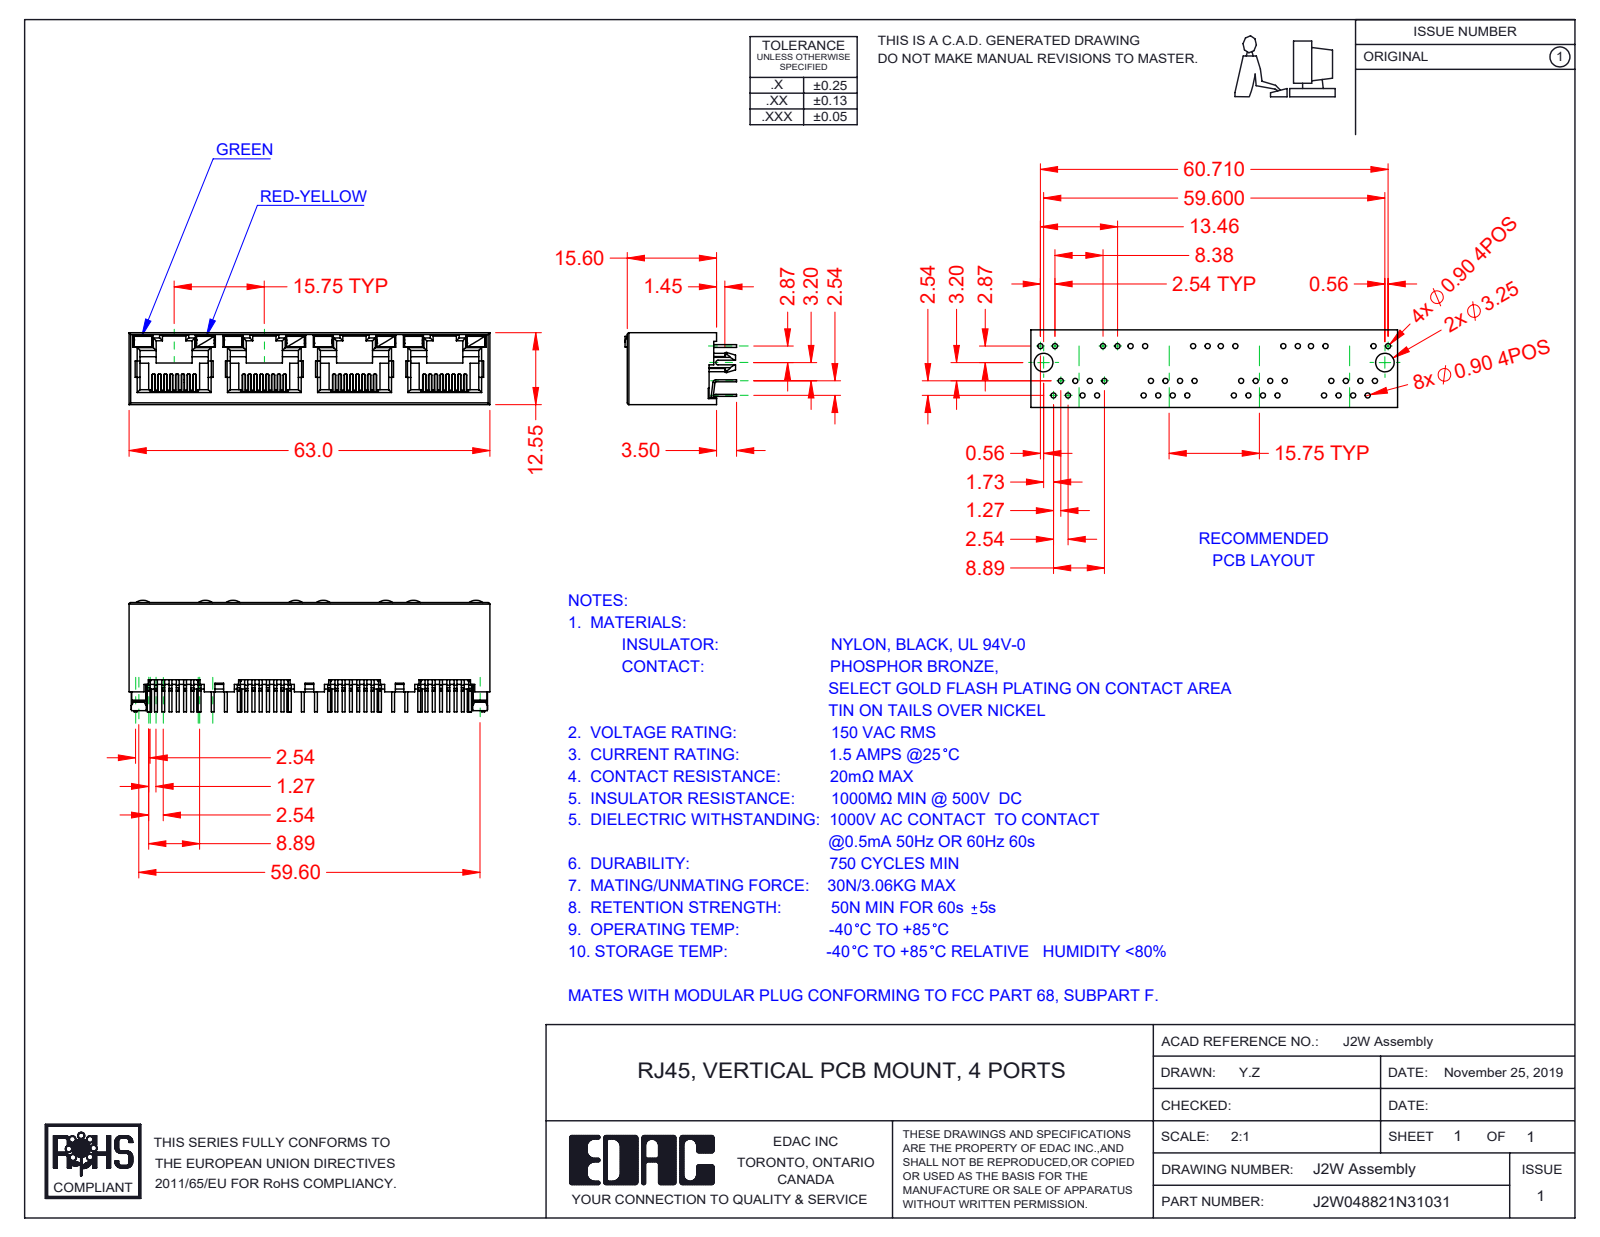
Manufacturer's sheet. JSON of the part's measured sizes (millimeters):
{"part_name": "J2W048821N38131; 2W LED RH_8-Red-Yellow; 2W Contacts; 2W Insulator (+2 more)", "step_written_by": "SolidWorks 2016 (CONFIG_CONTROL_DESIGN)", "units": "millimeters", "bodies": {"solids": 45, "faces": 3139, "planar": 2600, "cylindrical": 481, "other": 58}, "overall_size": [63, 19.5, 12.55], "volume_mm3": 5335, "surface_area_mm2": 13144, "partial_cylinders_radius": [[0.15, 64], [0.2, 29], [0.5, 28], [0.3, 14], [0.45, 8], [2, 8], [0.25, 2], [1.5, 2]], "face_to_face_distances": [12.55, 11.9, 0.65, 15.75, 0.36, 1.5, 0.78, 0.6, 11.3, 31.5]}
